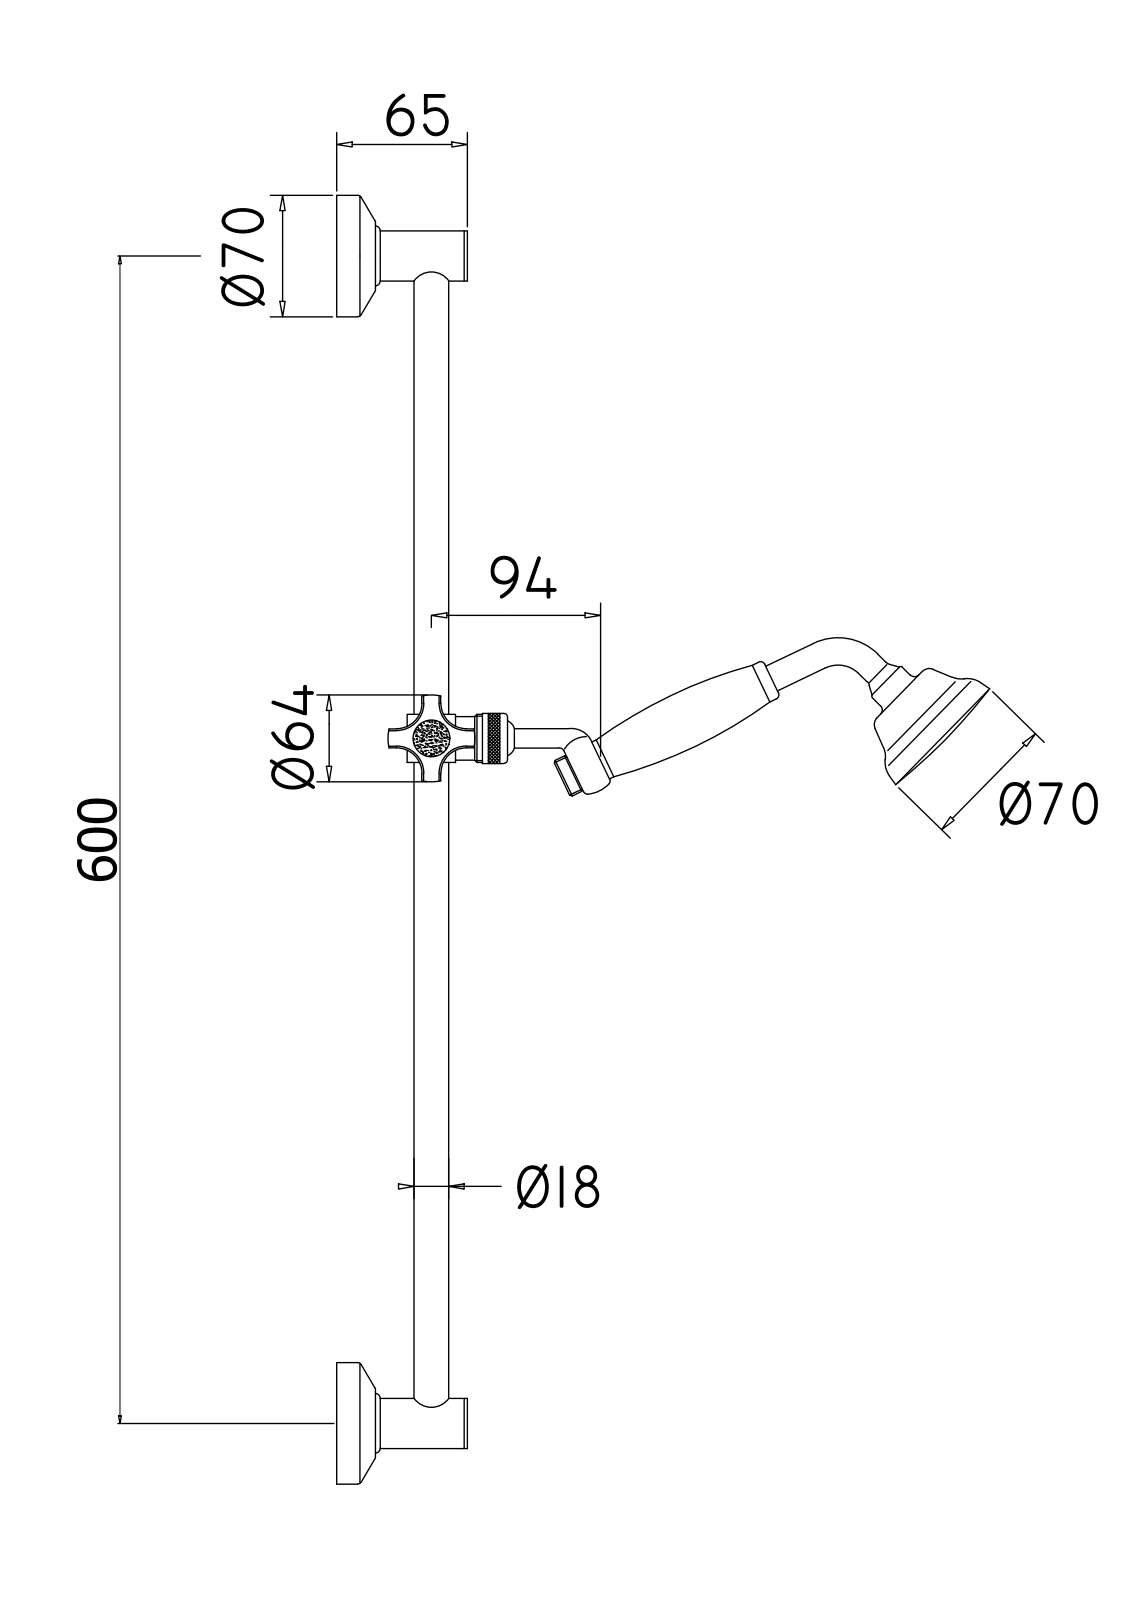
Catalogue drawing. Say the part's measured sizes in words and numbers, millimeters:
The part is named "ZSAL070CR". Its 3-D file was written by "CREO PARAMETRIC BY PTC INC, 2020044 (CONFIG_CONTROL_DESIGN)". It is 2 solids with 613 faces: 103 planar, 245 cylindrical and 265 other. Overall it measures 675 by 311.44 by 74 millimeters. Its volume is 217 666 cubic millimeters and its surface area 181 783 square millimeters. Round holes: 45 of diameter 1.2, 2 of diameter 6, 2 of diameter 12, 2 of diameter 12.2, 2 of diameter 14.5, 2 of diameter 20, 2 of diameter 69, 1 of diameter 10, 1 of diameter 10.5, 1 of diameter 13, 1 of diameter 14.7, 1 of diameter 15.4. Round bosses or shafts: 3 of diameter 30, 2 of diameter 70, 2 of diameter 26.5, 2 of diameter 26.1, 2 of diameter 22, 2 of diameter 21, 2 of diameter 18, 2 of diameter 14. Partial cylindrical surfaces (rounded edges, fillets, slot ends): 14 of radius 0.5, 1 of radius 5.25, 1 of radius 11. The main face-to-face distances are 1.5, 42.5, 2, 44, 31.5, 20.5, 27.51, 9, 51.5, 53. The hole center spacings are 24, 19, 14, 17.23, 23.99, 14.01, 12.42, 18.37.
